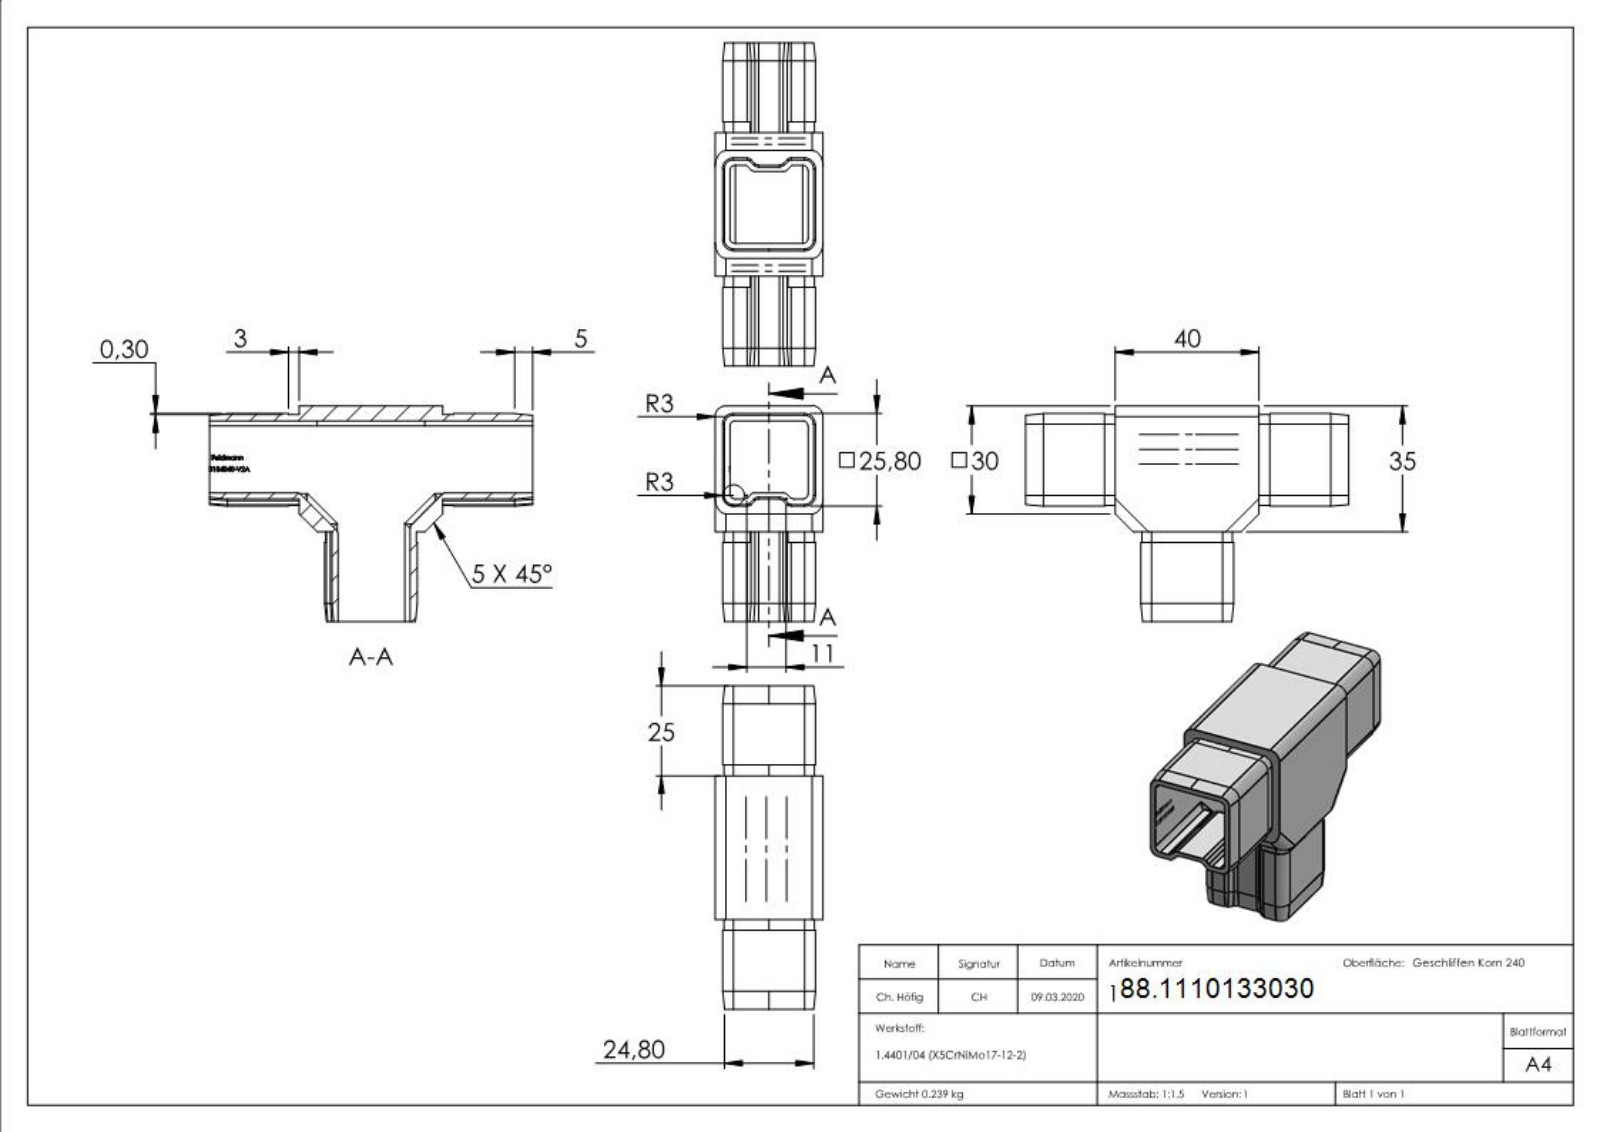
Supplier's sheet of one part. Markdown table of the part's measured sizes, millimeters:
| quantity | value |
| --- | --- |
| part name | 10133030 |
| STEP written by | SolidWorks 2015 (CONFIG_CONTROL_DESIGN) |
| units | millimeters |
| bodies | 1 solid, 473 faces (228 planar, 86 cylindrical, 159 other) |
| overall size | 90 × 60 × 30 |
| volume | 29 900 mm³ |
| surface area | 23 084 mm² |
| partial cylindrical surfaces (radius × count) | 1.5 × 39, 3 × 14, 2.7 × 8 |
| main face-to-face distances | 4.1, 2, 21.8, 23.8, 25.9, 2.1, 27.9, 25.8, 1.7, 30 |
